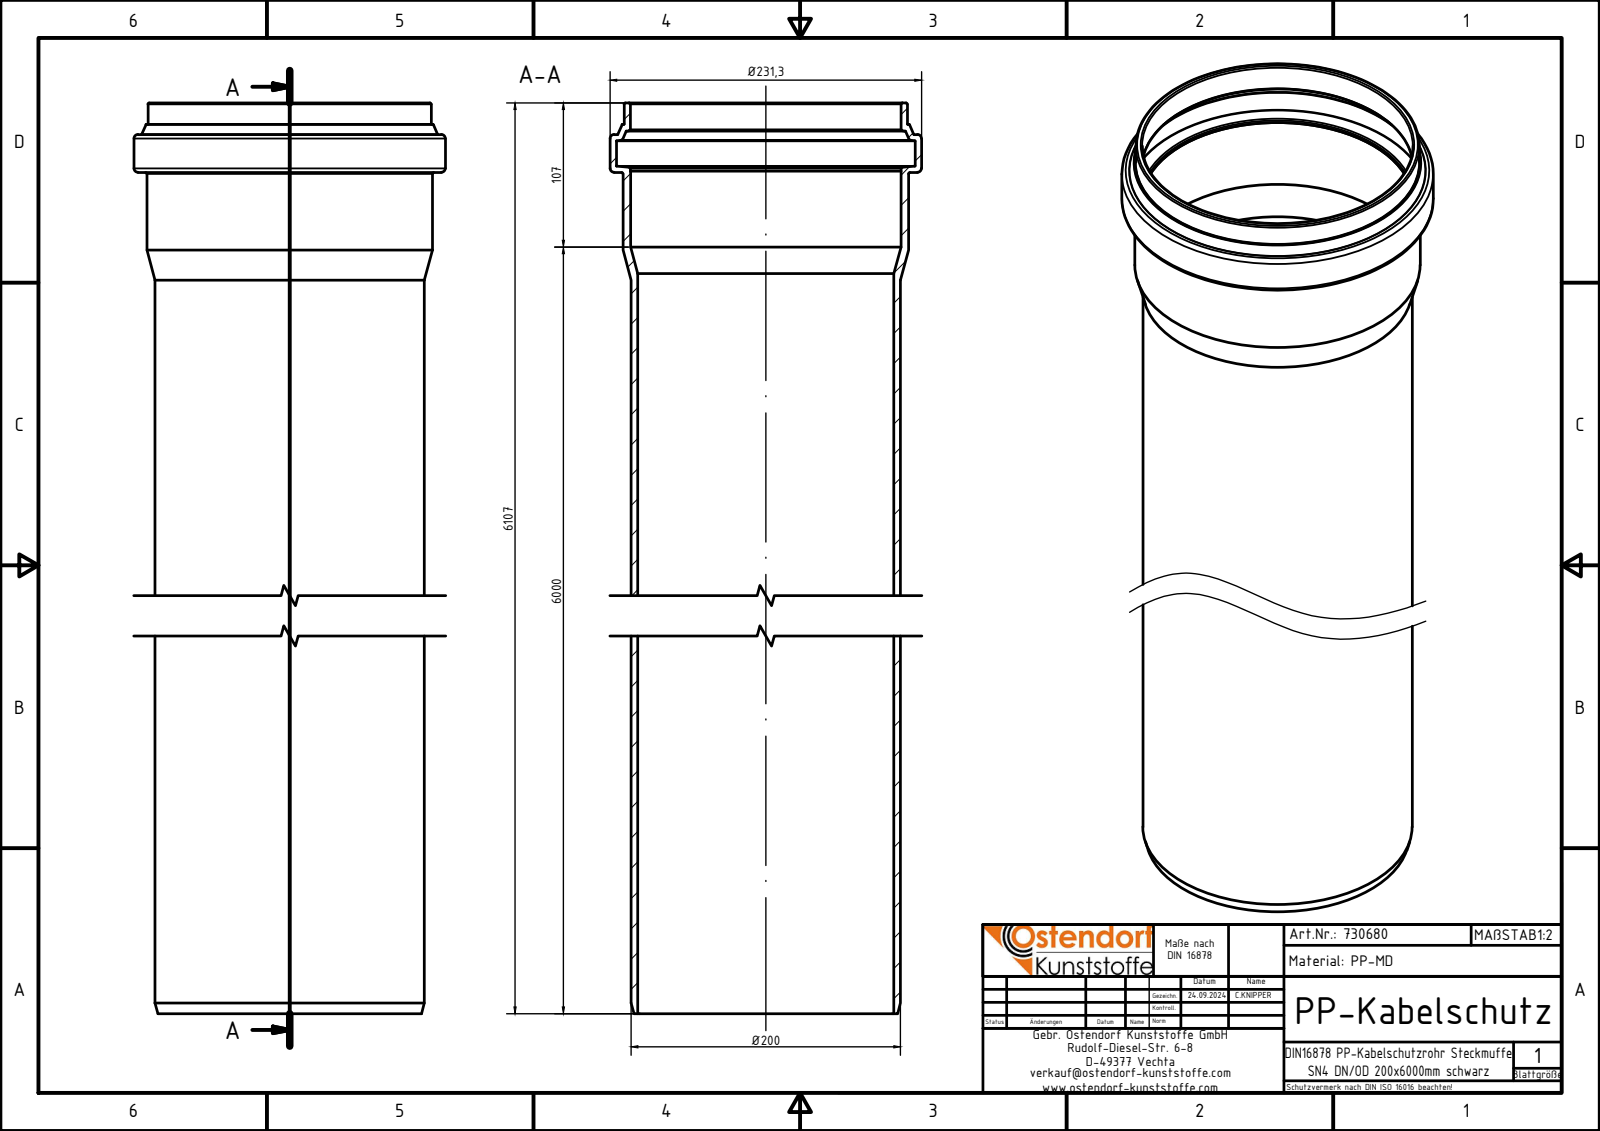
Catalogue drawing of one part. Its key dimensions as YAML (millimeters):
part_name: "730680z"
step_written_by: "Autodesk Inventor 2024 (AUTOMOTIVE_DESIGN)"
units: millimeters
bodies: {solids: 1, faces: 37, planar: 6, cylindrical: 9, other: 22}
overall_size: [6107, 231.3, 231.3]
volume: 18450000
surface_area: 7524000
round_holes:
  - {diameter: 190.2, count: 1}
  - {diameter: 200.8, count: 1}
  - {diameter: 201, count: 1}
  - {diameter: 221.9, count: 1}
round_bosses_or_shafts:
  - {diameter: 231.3, count: 1}
  - {diameter: 212, count: 1}
  - {diameter: 210.4, count: 1}
  - {diameter: 200, count: 1}
face_to_face_distances: [28.2, 51.7, 23.5, 6055.3, 6083.5, 6107, 6090.97, 35.67, 7.47, 16.03]
